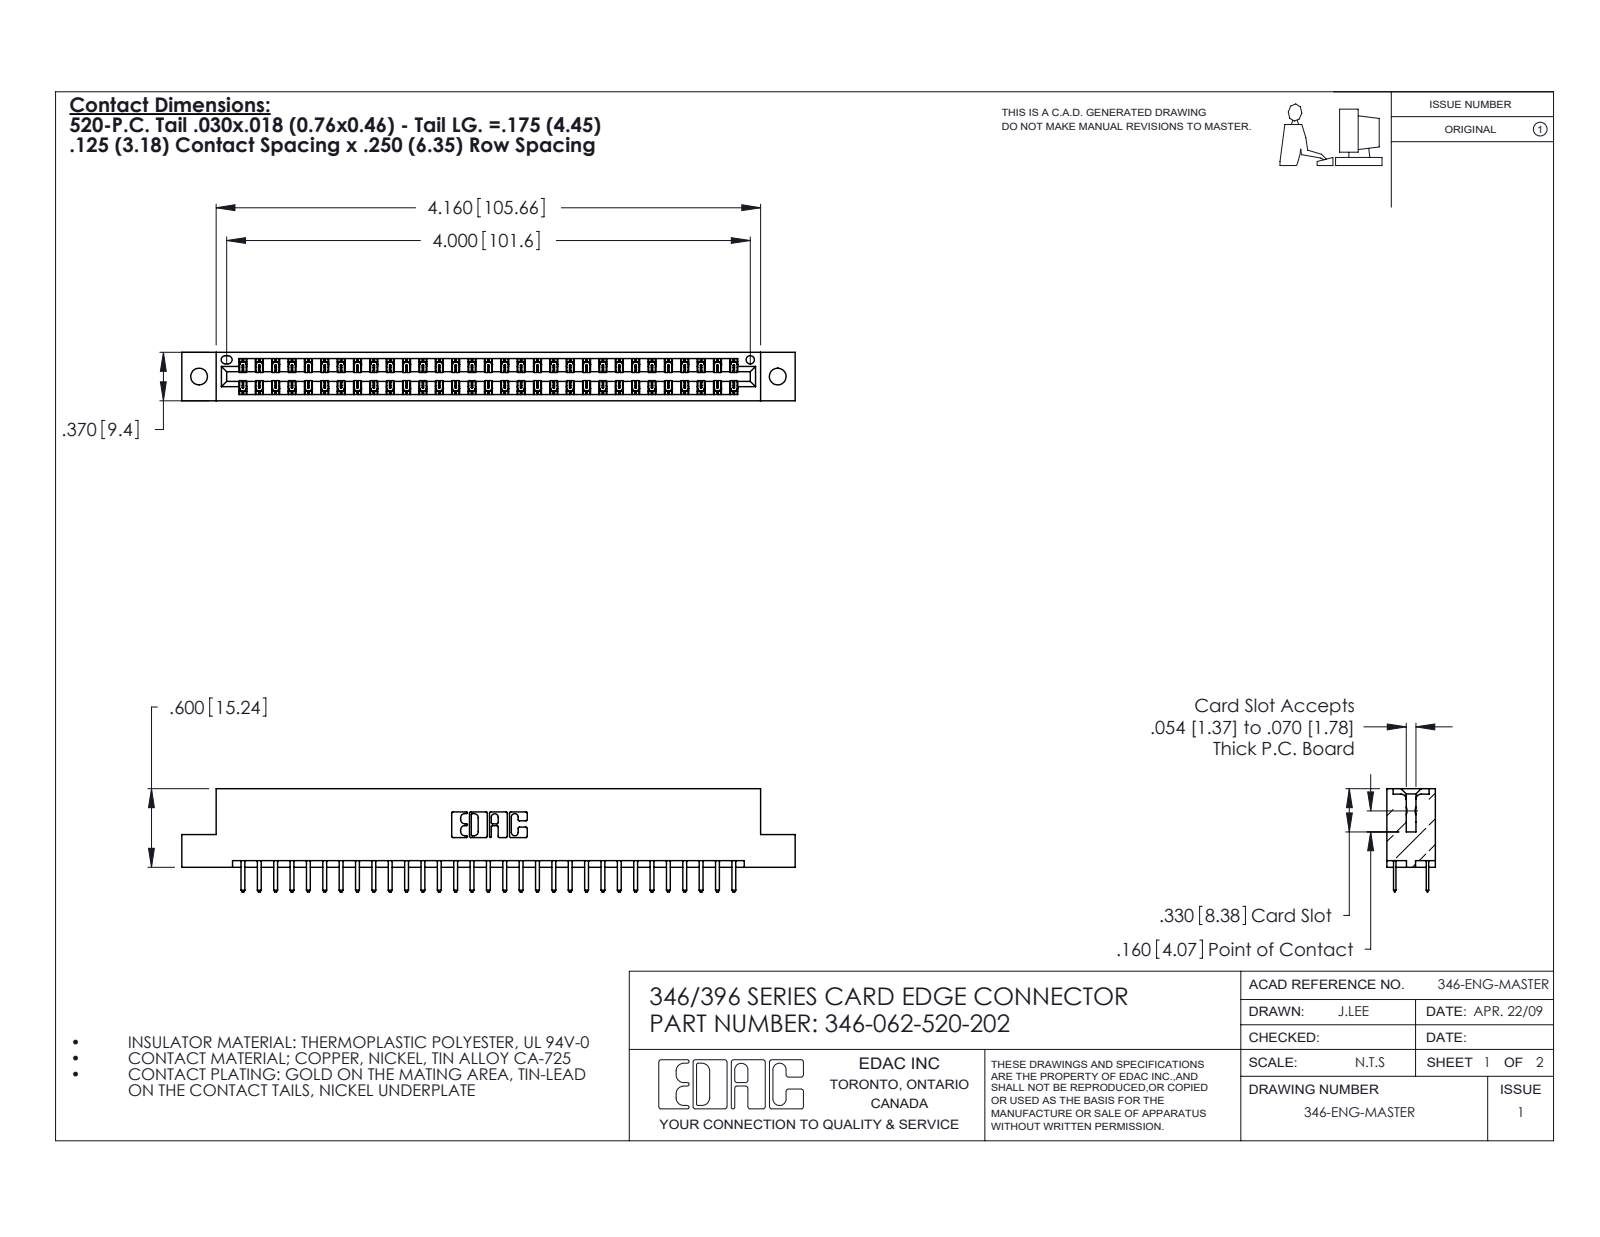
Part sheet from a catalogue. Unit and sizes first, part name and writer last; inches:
Units: inches
Overall size (bounding box): 4.685 × 0.788 × 0.37
Round holes (diameter × count): ⌀0.128 ×2, ⌀0.064 ×1
Partial cylindrical surfaces — rounded edges, fillets, slot ends (radius × count): R0.006 ×93, R0.01 ×66, R0.01 ×22, R0.007 ×6, R0.031 ×6, R0.026 ×3, R0.014 ×2, R0.022 ×2
Main face-to-face distances: 0.048, 0.322, 0.25, 0.37, 0.275, 0.072, 0.298, 0.025, 0.148, 0.222
Hole centre spacings: 0.246, 4.212, 4.42
Volume: 0.699 in³ · Surface area: 23.62 in²
Bodies: 63 solids, 3594 faces (2370 planar, 1224 cylindrical, 0 other)
Part name (STEP PRODUCT): 346 Part_Flush Mounting Lugs - 0.128 Dia; 346-062-520-202; 345-292-001_345-293-120
STEP written by: SolidWorks 2020 (CONFIG_CONTROL_DESIGN)
